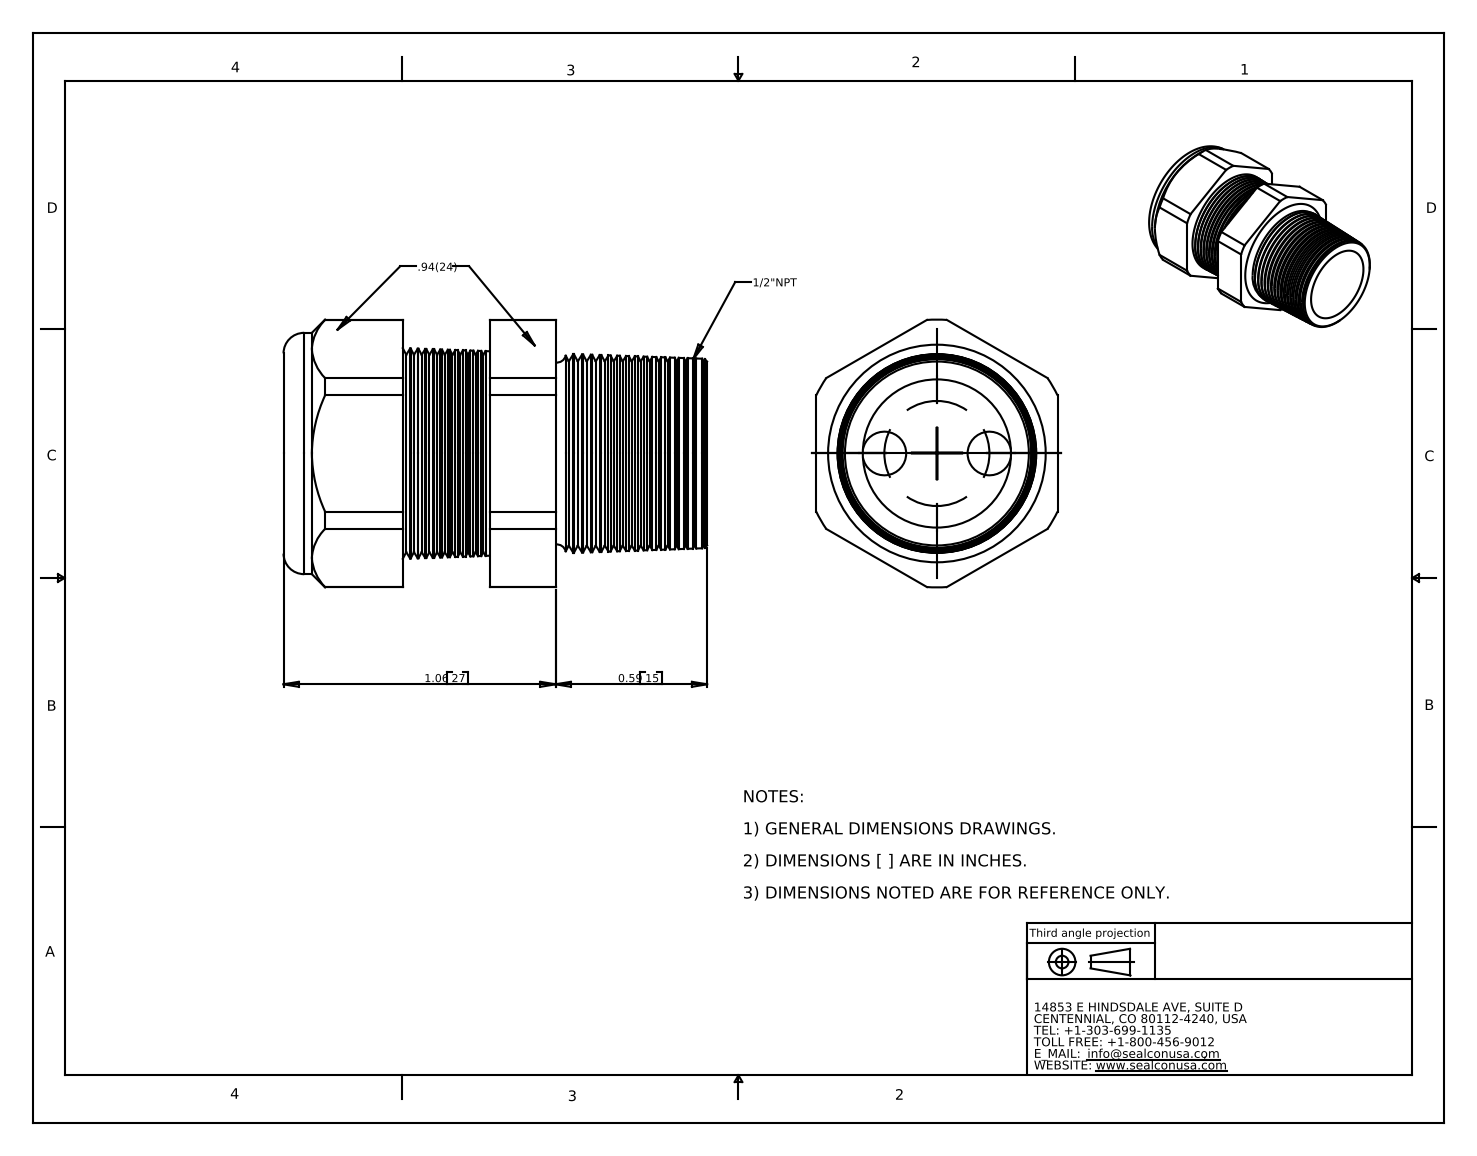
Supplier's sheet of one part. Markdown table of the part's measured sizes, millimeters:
| quantity | value |
| --- | --- |
| part name | CD13N8-GY |
| STEP written by | SolidWorks 2007 (CONFIG_CONTROL_DESIGN) |
| units | millimeters |
| bodies | 2 solids, 208 faces (20 planar, 24 cylindrical, 164 other) |
| overall size | 39.9 × 26.5 × 23.9 |
| volume | 9 230 mm³ |
| surface area | 7 471 mm² |
| round holes (diameter × count) | 4.3 × 2, 14.7 × 1, 15.2 × 1 |
| round bosses / shafts (diameter × count) | 23.9 × 1 |
| partial cylindrical surfaces (radius × count) | 13.3 × 1 |
| main face-to-face distances | 23.9, 11.5, 2.9, 8.6, 8.4, 11.3, 19.9, 0.5, 8.9, 11.8 |
| hole center spacings | 5.2, 10.4 |
